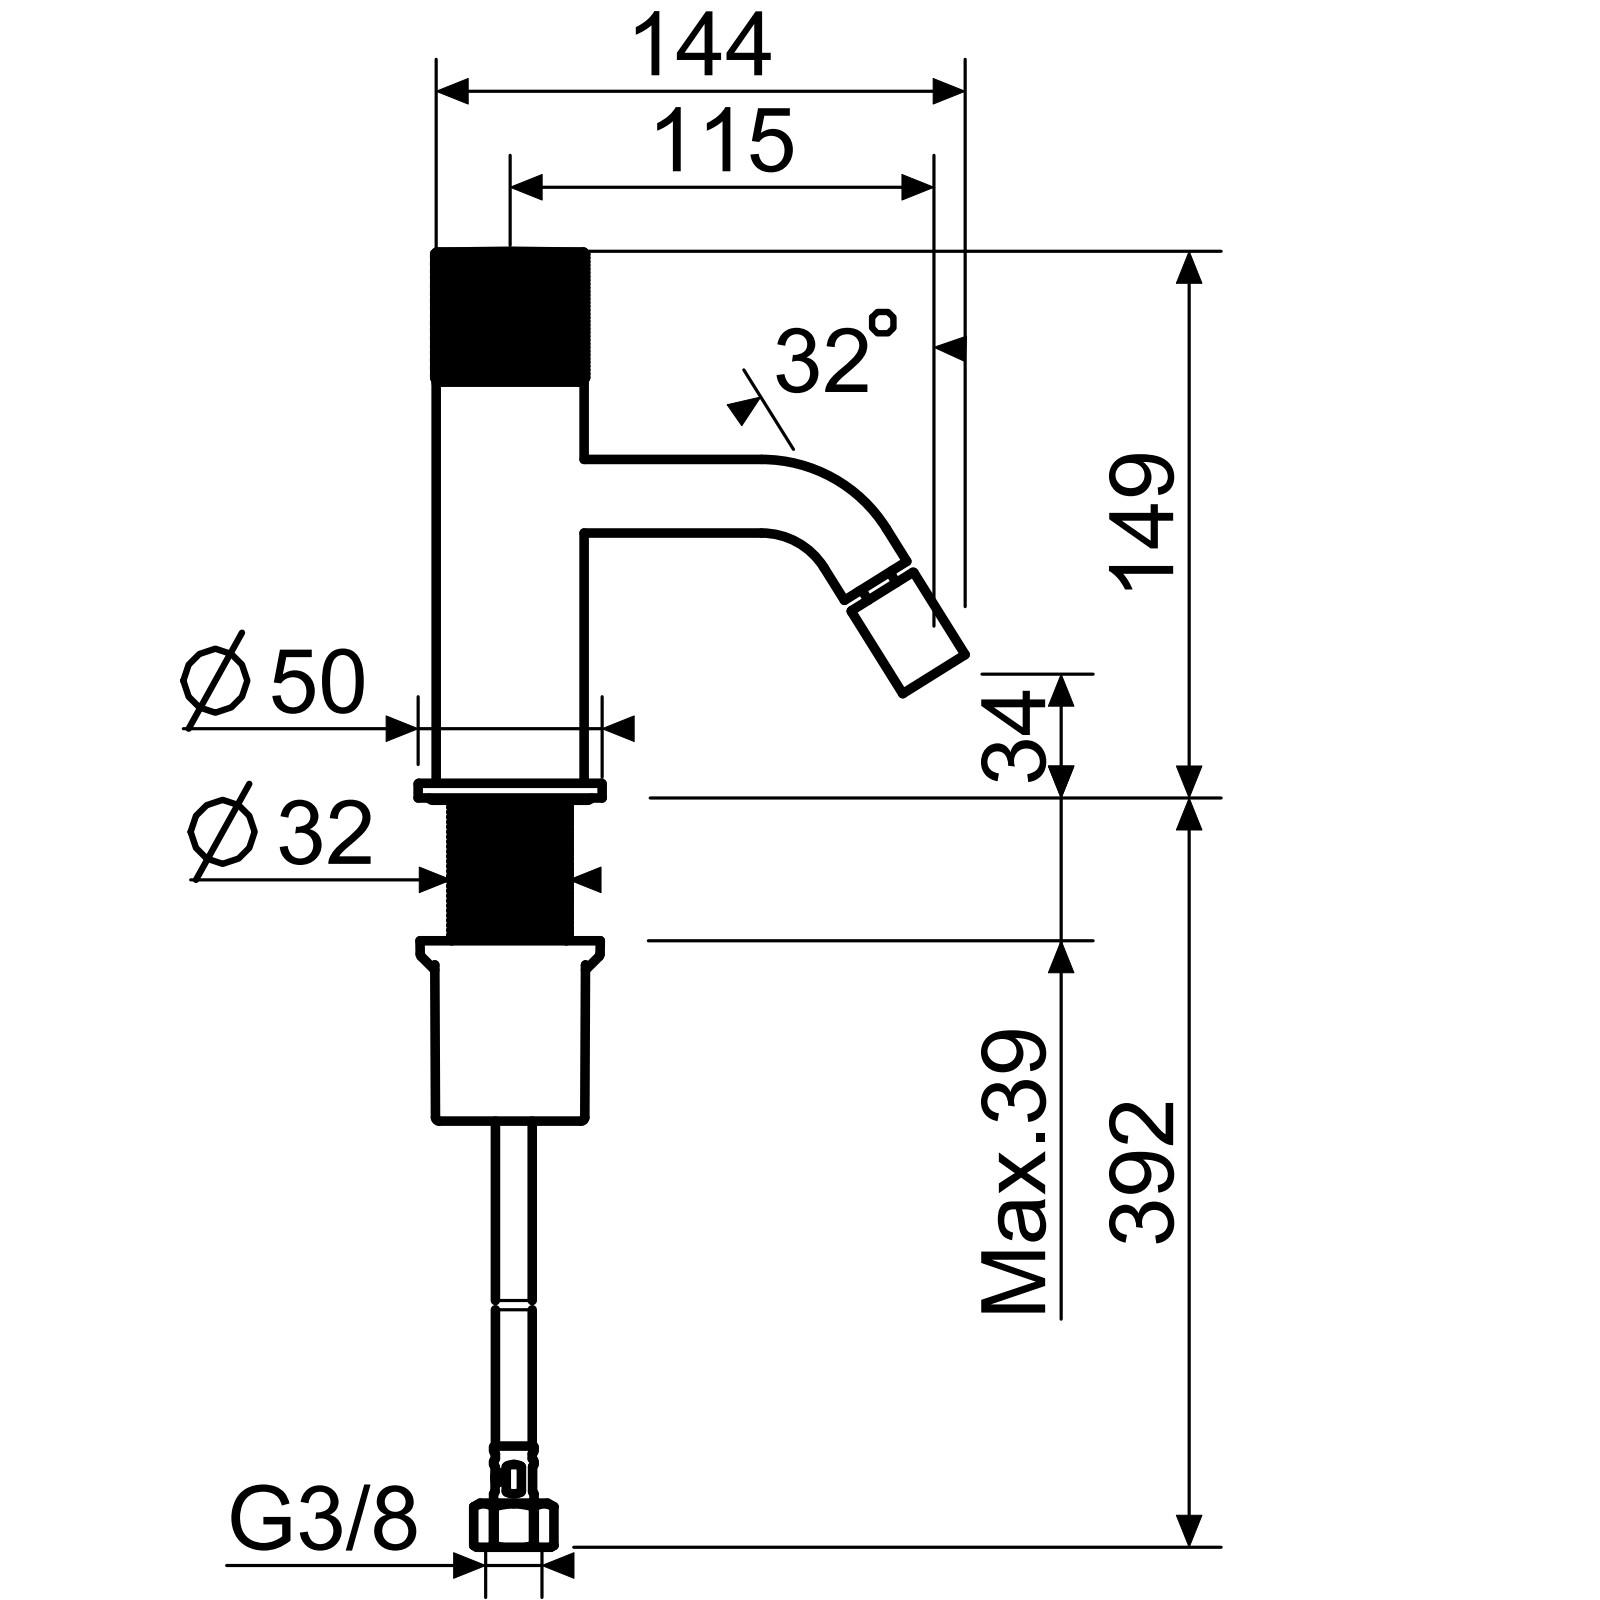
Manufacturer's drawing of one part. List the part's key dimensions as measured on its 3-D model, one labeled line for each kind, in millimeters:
Part name (STEP PRODUCT): ALOG300C001; ALOG007C004; ALOG300W001; SARPKC0020 (+8 more)
STEP written by: CREO PARAMETRIC BY PTC INC, 2022164 (CONFIG_CONTROL_DESIGN)
Units: millimetres
Bodies: 14 solids, 6664 faces (3032 planar, 1282 cylindrical, 2350 other)
Overall size (bounding box): 156.42 × 149.33 × 50
Volume: 79 848 mm³ · Surface area: 73 646 mm²
Round holes (diameter × count): ⌀4.2 ×2, ⌀5 ×2, ⌀5.1 ×1, ⌀5.3 ×1, ⌀6.5 ×1, ⌀8 ×1, ⌀9 ×1, ⌀10.3 ×1, ⌀11.8 ×1, ⌀12.2 ×1, ⌀13 ×1, ⌀13.5 ×1
Round bosses / shafts (diameter × count): ⌀20 ×2, ⌀9 ×2, ⌀50 ×1, ⌀40.2 ×1, ⌀40 ×1, ⌀37.8 ×1, ⌀32 ×1, ⌀18 ×1
Partial cylindrical surfaces — rounded edges, fillets, slot ends (radius × count): R1 ×2, R2.5 ×2, R3 ×2, R1.5 ×1, R4 ×1, R6.5 ×1, R10 ×1, R16 ×1
Main face-to-face distances: 2, 4, 145.8, 141.8, 28.42, 2.75, 143.8, 28.44, 99.8, 110.95
